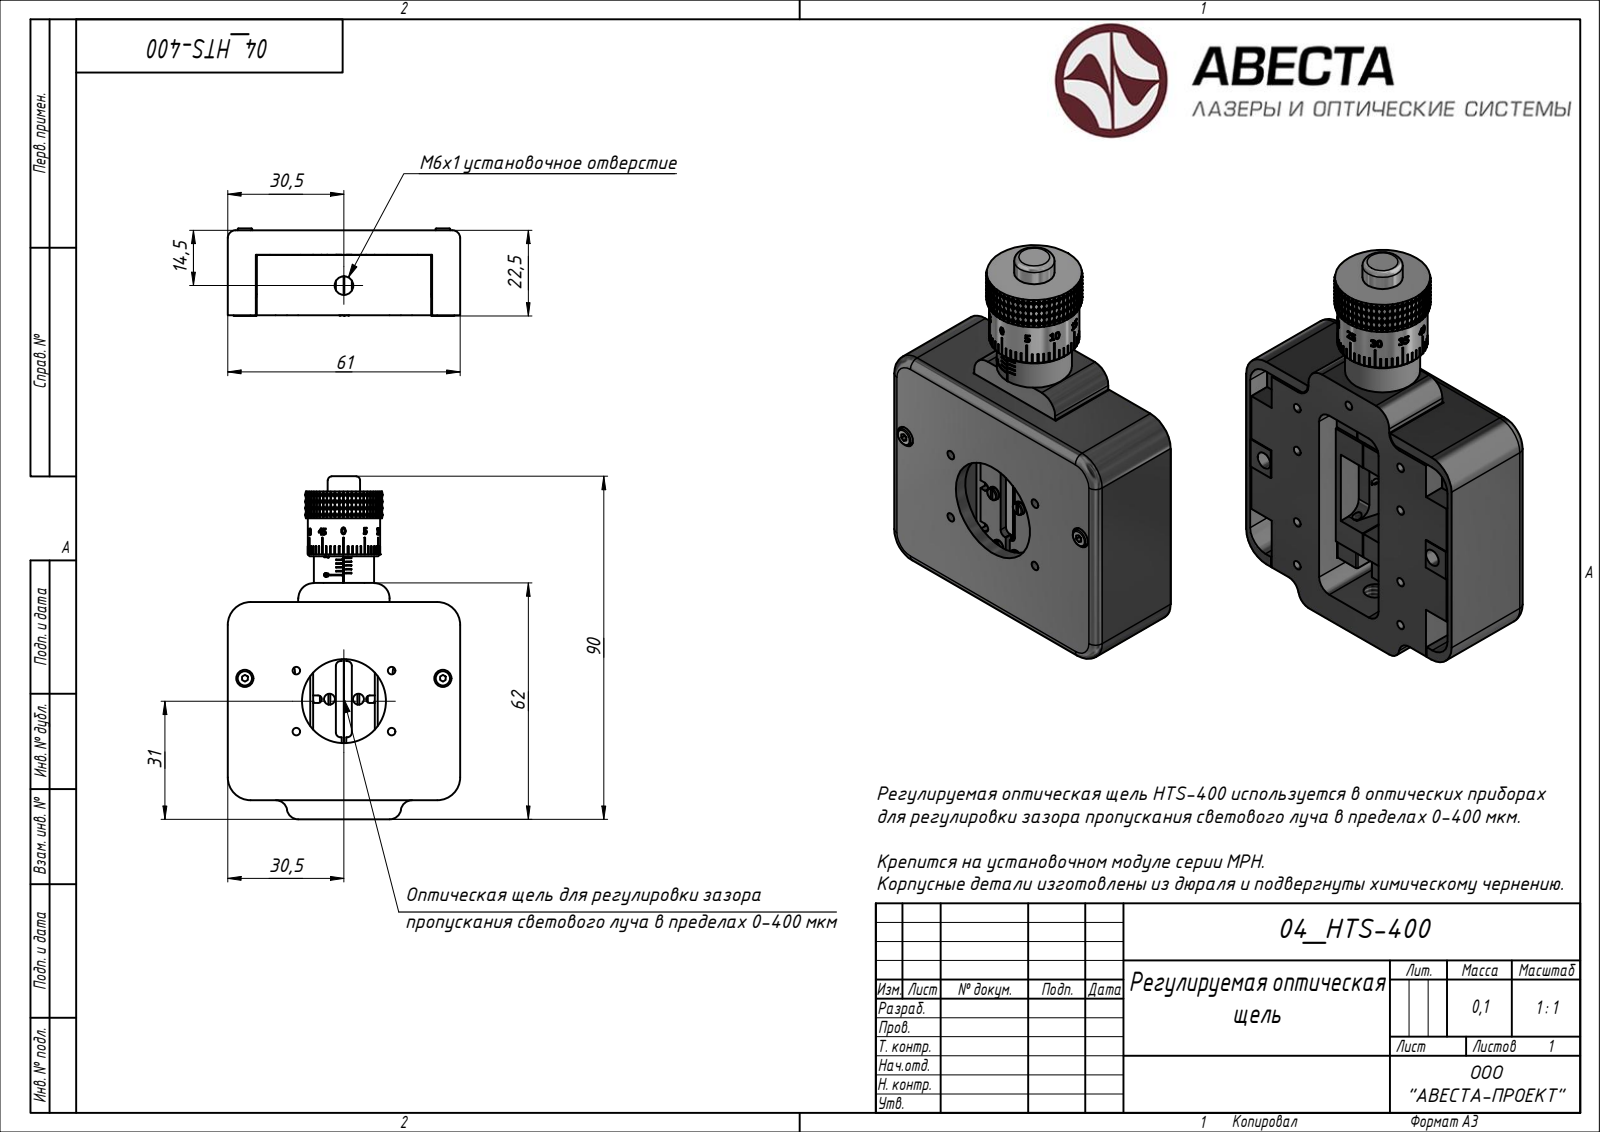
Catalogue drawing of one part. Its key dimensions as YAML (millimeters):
step_written_by: "Rhino 7.34 (AUTOMOTIVE_DESIGN)"
units: millimeters
bodies: {solids: 33, faces: 3021, planar: 2170, cylindrical: 522, other: 329}
overall_size: [90, 61, 23]
volume: 57324
surface_area: 43344
round_holes:
  - {diameter: 2.8, count: 16}
  - {diameter: 5, count: 16}
  - {diameter: 2.01, count: 13}
  - {diameter: 3, count: 10}
  - {diameter: 1.8, count: 6}
  - {diameter: 2.01, count: 5}
  - {diameter: 2, count: 4}
  - {diameter: 1.22, count: 3}
  - {diameter: 1.5, count: 3}
  - {diameter: 6.5, count: 3}
  - {diameter: 1.6, count: 2}
  - {diameter: 2.3, count: 2}
round_bosses_or_shafts:
  - {diameter: 2.85, count: 6}
  - {diameter: 1.6, count: 6}
  - {diameter: 3.8, count: 2}
  - {diameter: 2, count: 2}
  - {diameter: 20, count: 1}
  - {diameter: 19, count: 1}
  - {diameter: 15.8, count: 1}
  - {diameter: 8.5, count: 1}
partial_cylinders:
  - {radius: 3, count: 26}
  - {radius: 0.3, count: 16}
  - {radius: 1, count: 6}
  - {radius: 1.25, count: 4}
  - {radius: 2, count: 4}
  - {radius: 2.5, count: 4}
  - {radius: 4.5, count: 4}
  - {radius: 6, count: 4}
face_to_face_distances: [6.5, 15.8, 2.8, 22.3, 19.5, 3.7, 29.2, 1.5, 1.2, 59.8]
hole_center_spacings: [11, 20.9, 31.1, 6, 21.74, 26, 31.67, 6.04]
